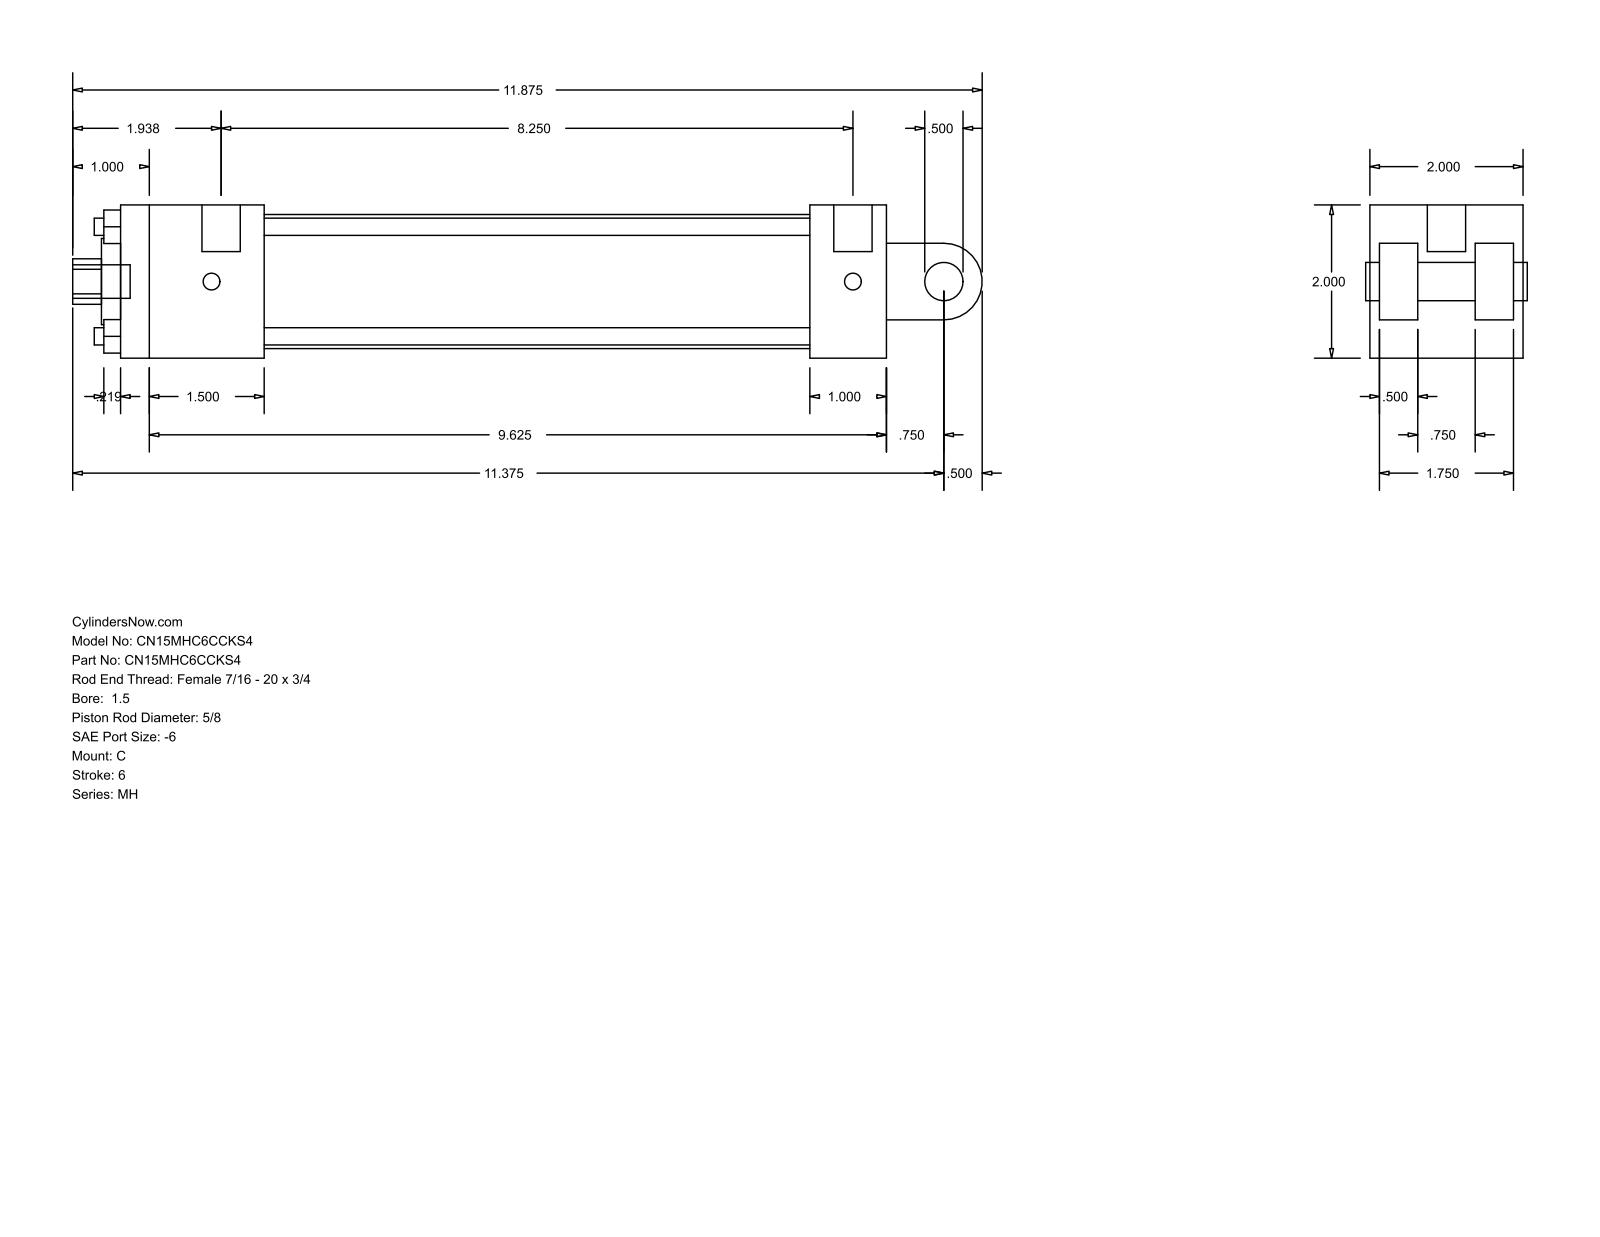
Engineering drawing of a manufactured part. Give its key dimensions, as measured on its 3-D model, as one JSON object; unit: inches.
{"part_name": "MH_C__0150_0.625", "step_written_by": "GSSL Pune (CONFIG_CONTROL_DESIGN)", "units": "inches", "bodies": {"solids": 0, "faces": 99, "planar": 70, "cylindrical": 29, "other": 0}, "overall_size": [11.875, 2, 2], "round_holes": [[0.225, 4], [0.219, 2], [0.5, 1], [0.625, 1], [1.125, 1], [1.75, 1]], "round_bosses_or_shafts": [[0.5, 2], [0.219, 2], [0.437, 1]], "partial_cylinders_radius": [[0.297, 1], [0.5, 1]], "face_to_face_distances": [2, 0.5, 10, 0.125, 0.625, 1.375, 1.875, 1.25, 1.5, 1.875], "hole_center_spacings": [1.011, 1.43, 2.022]}
